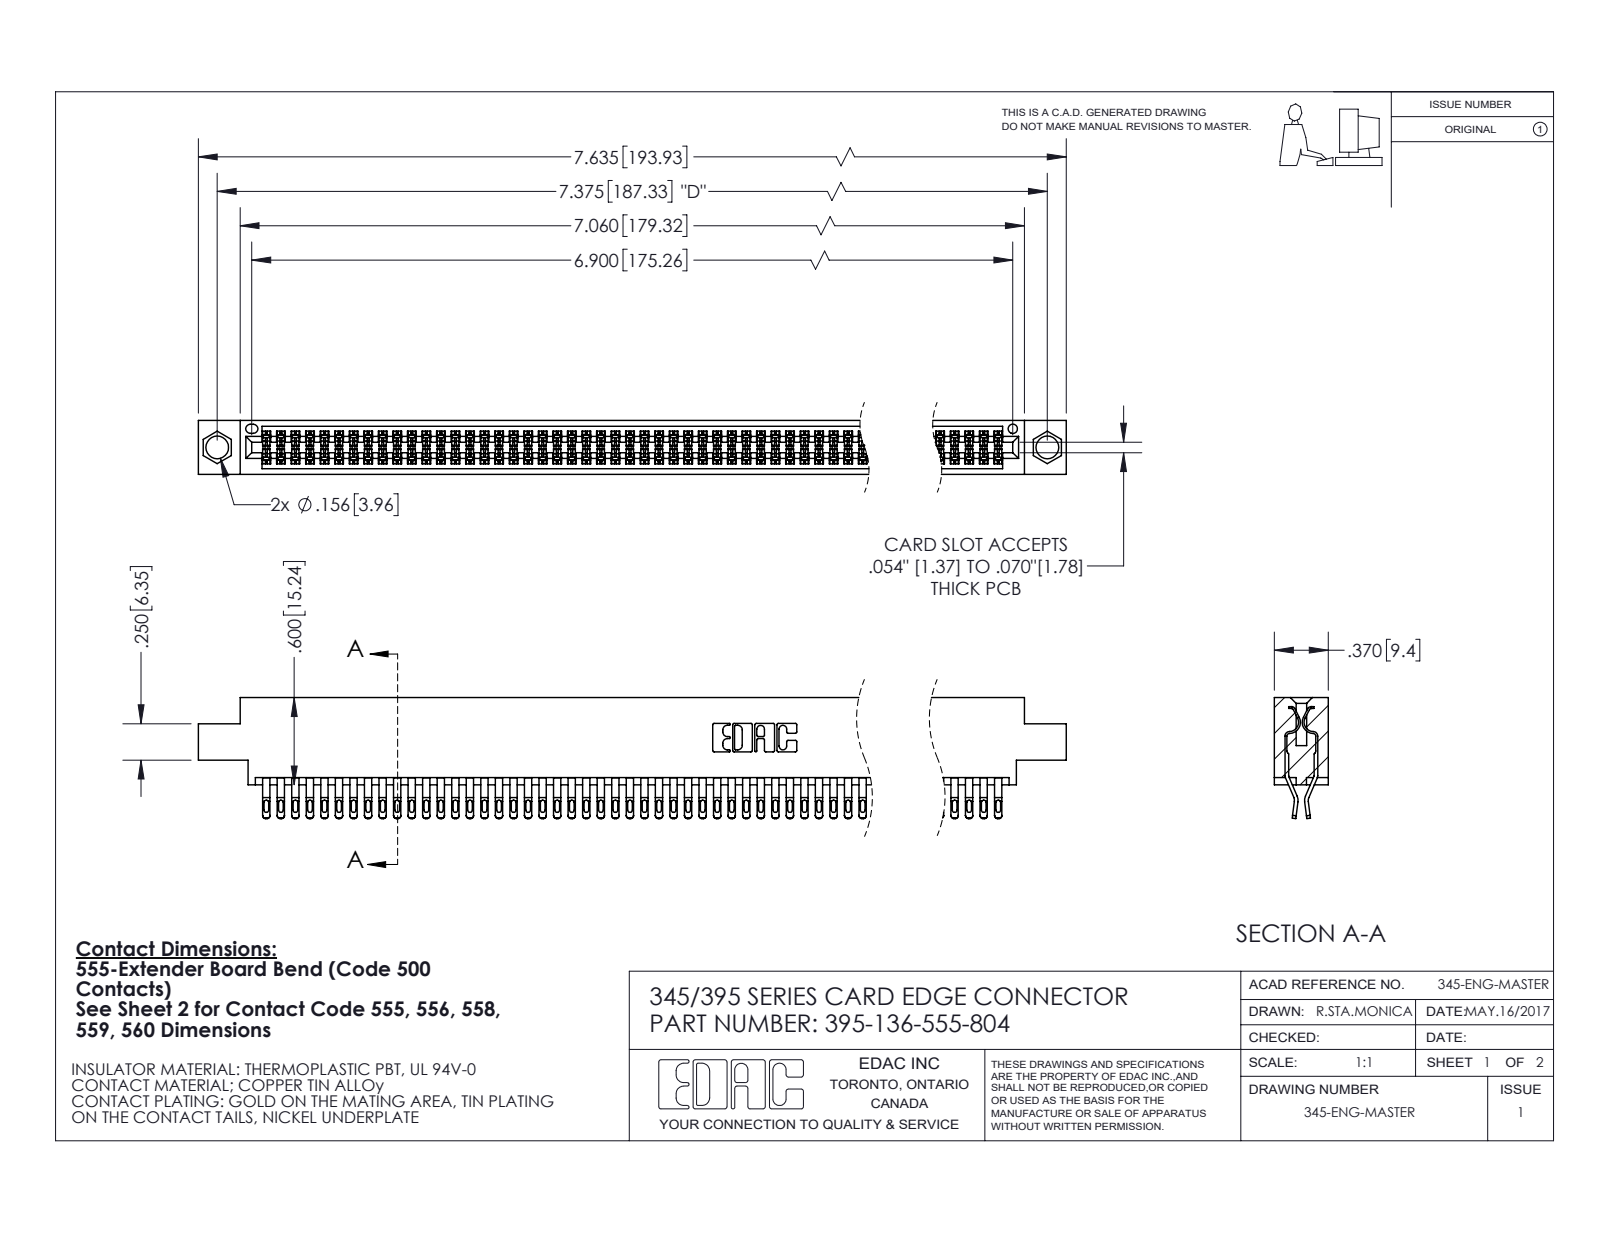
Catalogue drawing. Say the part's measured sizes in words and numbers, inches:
The part is named "345-292-001_555 Tail; 395-136-555-804; 345 Part_0.170 Offset - 0.156 Dia-TI". Its 3-D file was written by "SolidWorks 2020 (CONFIG_CONTROL_DESIGN)". It is 137 solids with 7760 faces: 4314 planar, 3446 cylindrical and 0 other. Overall it measures 7.635 by 0.832 by 0.37 inches. Its volume is 1.175 cubic inches and its surface area 47.02 square inches. Round holes: 2 of diameter 0.156, 1 of diameter 0.064. Partial cylindrical surfaces (rounded edges, fillets, slot ends): 340 of radius 0.016, 272 of radius 0.006, 272 of radius 0.02, 22 of radius 0.01, 6 of radius 0.007, 6 of radius 0.031, 3 of radius 0.026, 2 of radius 0.01. The main face-to-face distances are 0.072, 0.298, 0.025, 0.37, 0.2, 0.098, 0.272, 0.225, 0.175, 0.149. The hole center spacings are 0.27, 7.139, 7.375.
